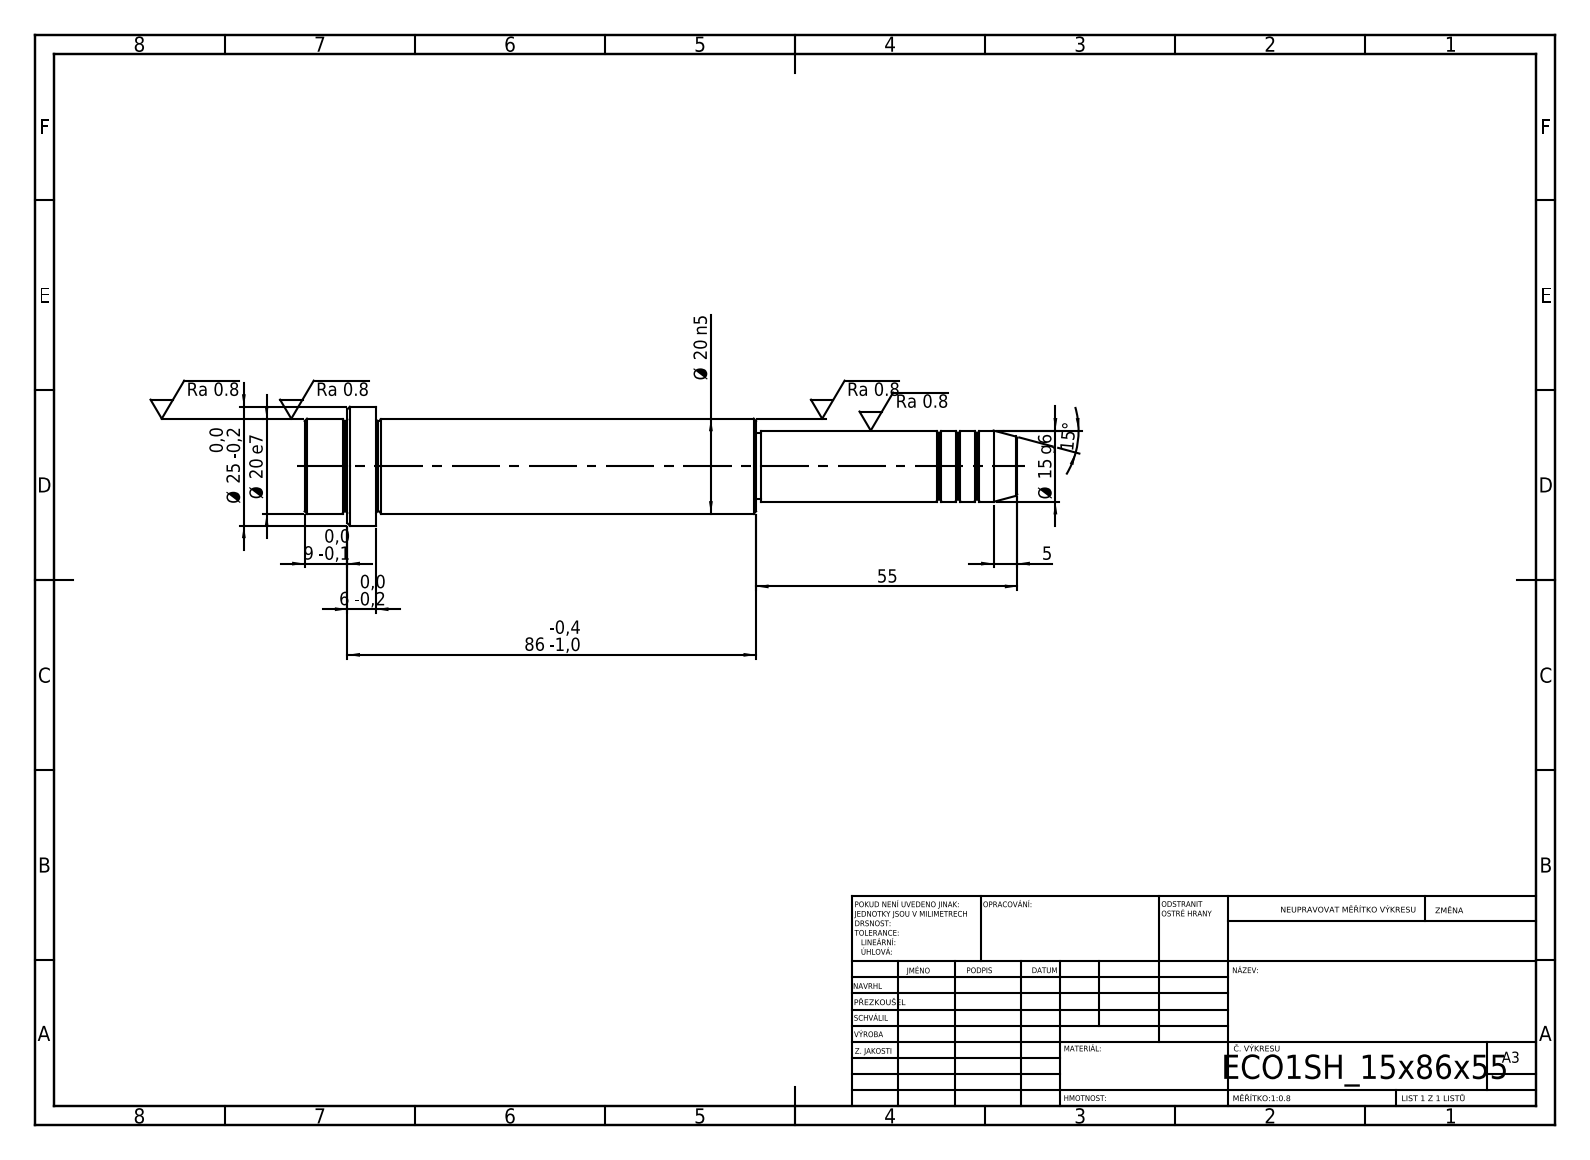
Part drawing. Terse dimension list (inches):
written by: SolidWorks 2019 (CONFIG_CONTROL_DESIGN)
unit: in
bodies: 1 solid, 52 faces (6 planar, 16 cylindrical, 30 other)
size: 5.906 × 0.984 × 0.984
volume: 2.461 in³; area: 15 in²
bosses: 1× ⌀0.984, 1× ⌀0.787, 1× ⌀0.591, 1× ⌀0.551
face distances: 0.591, 0.236, 0.354, 3.15, 3.386, 3.74, 2.165, 5.315, 5.551, 5.906
